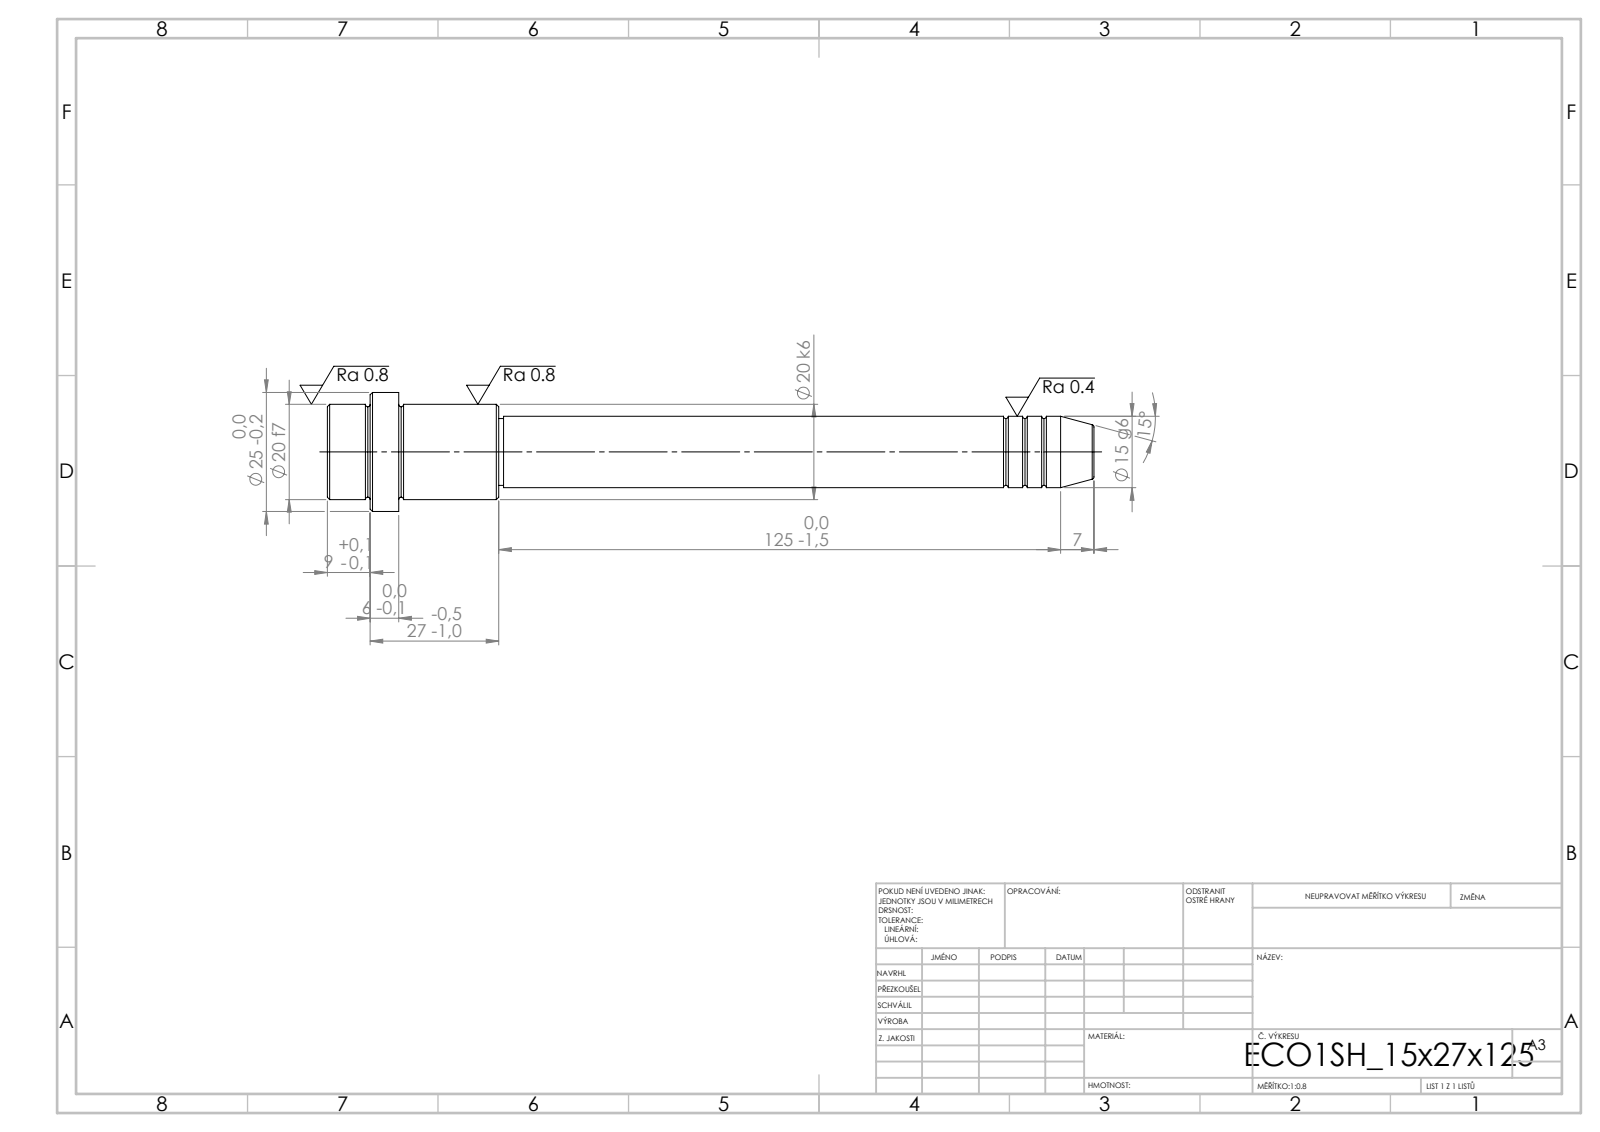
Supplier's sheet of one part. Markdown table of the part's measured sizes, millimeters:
| quantity | value |
| --- | --- |
| STEP written by | SolidWorks 2019 (CONFIG_CONTROL_DESIGN) |
| units | millimeters |
| bodies | 1 solid, 52 faces (6 planar, 16 cylindrical, 30 other) |
| overall size | 161 × 25 × 25 |
| volume | 34 025 mm³ |
| surface area | 9 234 mm² |
| round bosses / shafts (diameter × count) | 25 × 1, 20 × 1, 15 × 1, 14 × 1 |
| main face-to-face distances | 15, 6, 9, 21, 27, 36, 125, 146, 152, 161 |
